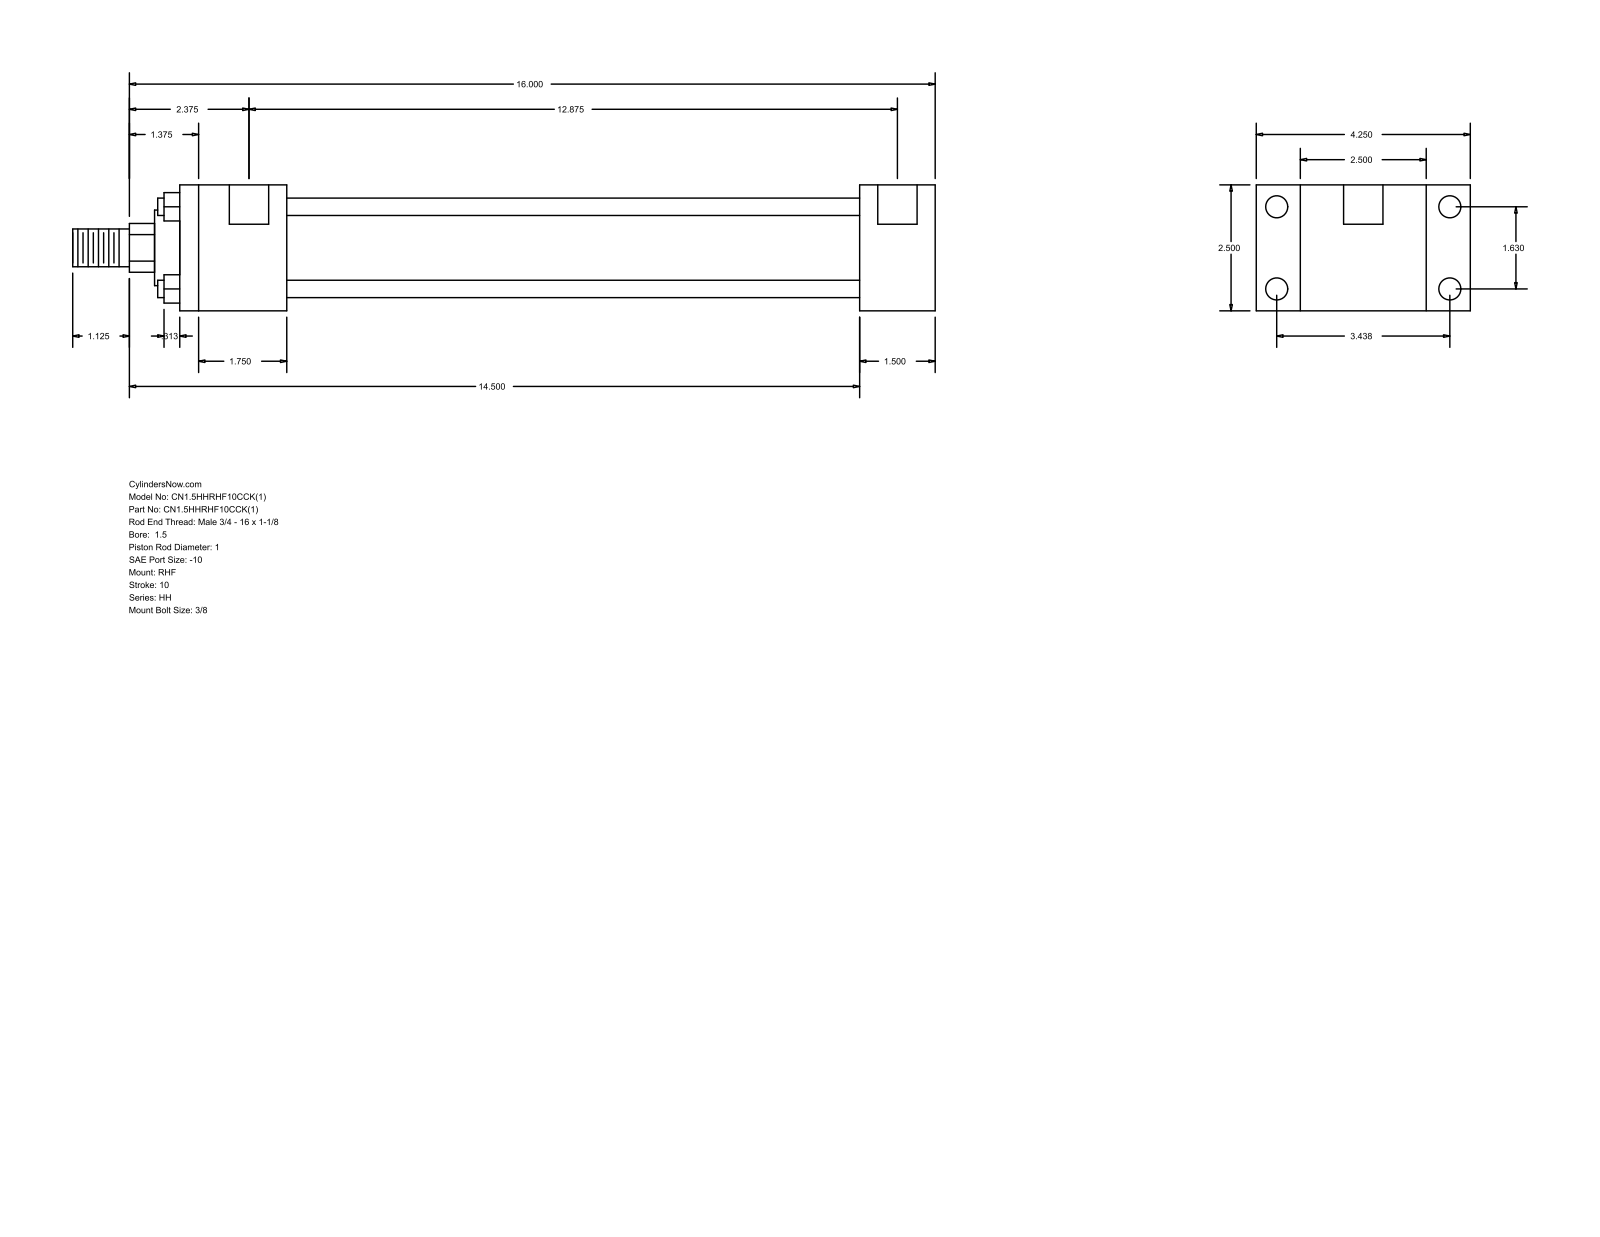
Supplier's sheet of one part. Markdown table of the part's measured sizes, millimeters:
| quantity | value |
| --- | --- |
| part name | HH_RHF__0150_1 |
| STEP written by | GSSL Pune (CONFIG_CONTROL_DESIGN) |
| units | millimeters |
| bodies | 0 solids, 88 faces (60 planar, 28 cylindrical, 0 other) |
| overall size | 434.98 × 107.95 × 63.5 |
| round holes (diameter × count) | 5.56 × 4, 11.13 × 4, 19.84 × 2 |
| round bosses / shafts (diameter × count) | 8.76 × 4, 44.45 × 1, 38.1 × 1, 25.4 × 1, 19.05 × 1 |
| partial cylindrical surfaces (radius × count) | 12.29 × 1 |
| main face-to-face distances | 63.5, 22.23, 85.73, 38.1, 107.96, 288.92, 327.02, 53.98, 342.9, 381 |
| hole center spacings | 1.59, 41.4, 87.32, 96.64, 328.61, 330.2, 327.02 |
